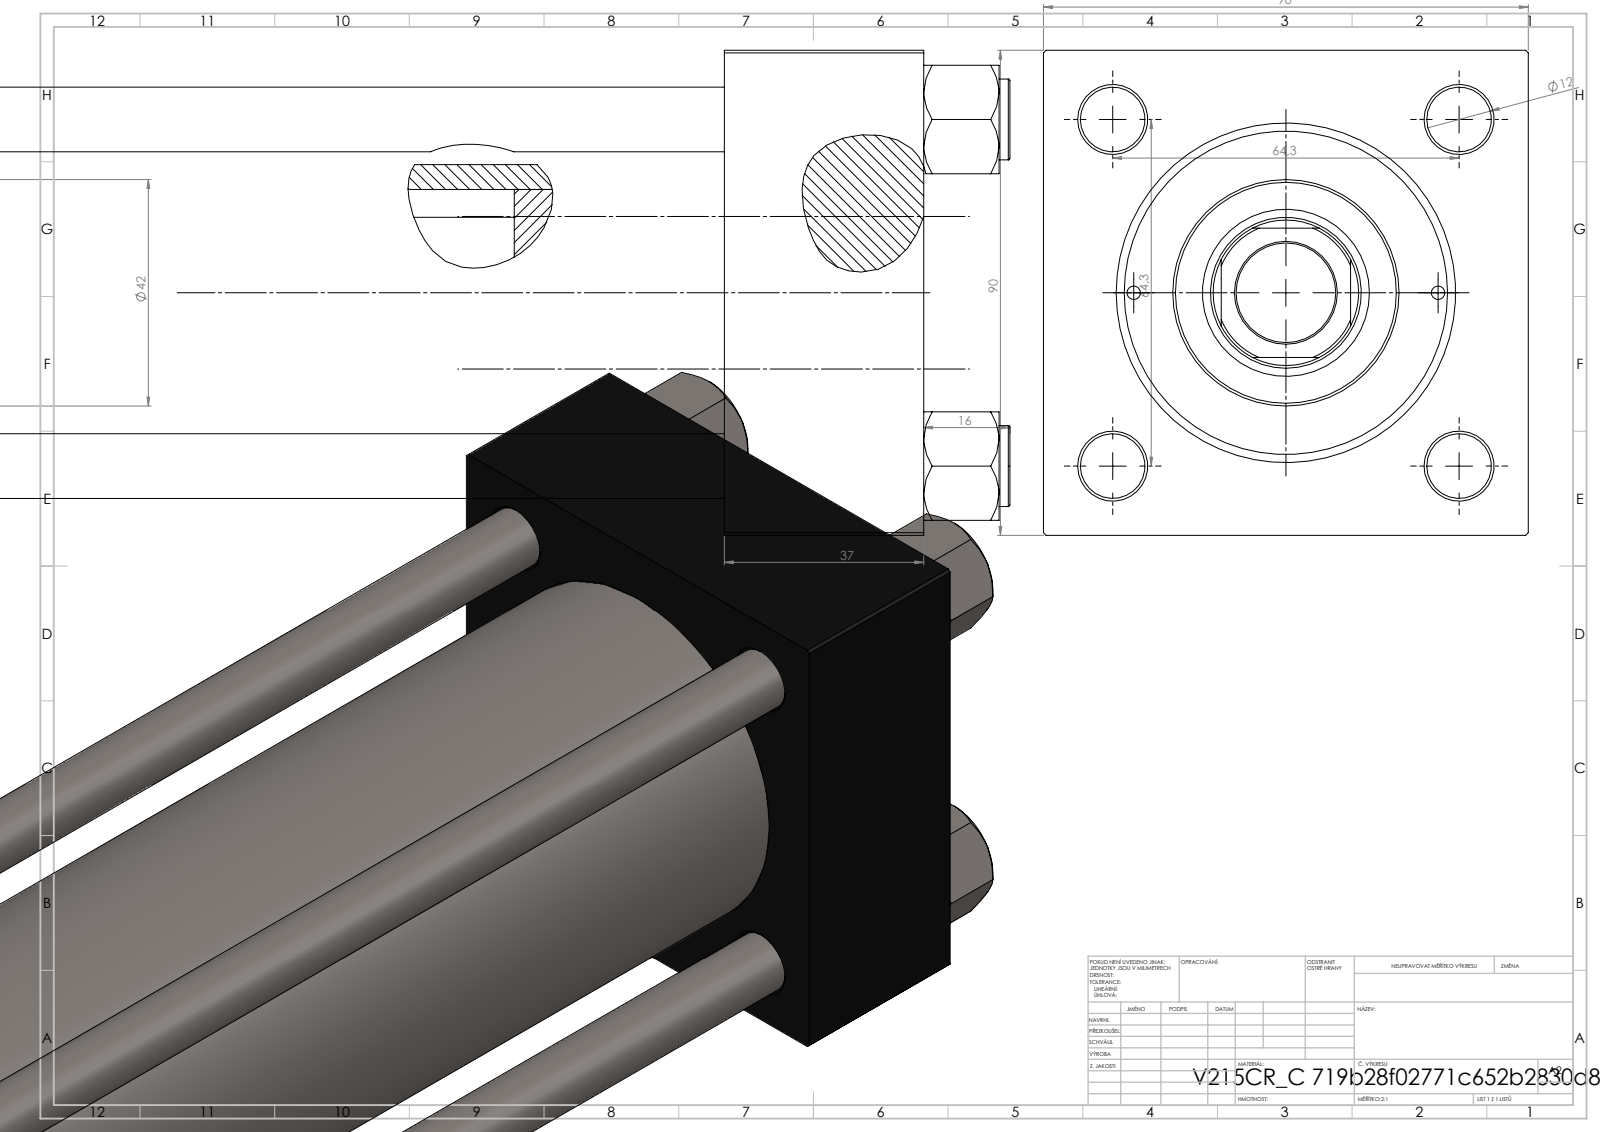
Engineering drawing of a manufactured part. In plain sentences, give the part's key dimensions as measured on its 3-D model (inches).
The part is named "V215CR_C_Body; NUT_M5_C; V215CR_C_TYCINKA; V215CR_VCP_C (+1 more)". Its 3-D file was written by "SolidWorks 2019 (CONFIG_CONTROL_DESIGN)". It is 11 solids with 1154 faces: 528 planar, 90 cylindrical and 536 other. Overall it measures 20.984 by 3.543 by 3.543 inches. Its volume is 91.84 cubic inches and its surface area 612 square inches. Round holes: 4 of diameter 0.472, 2 of diameter 0.098, 2 of diameter 0.276, 2 of diameter 0.825, 2 of diameter 1.181, 1 of diameter 0.728, 1 of diameter 1.102, 1 of diameter 1.22, 1 of diameter 1.969, 1 of diameter 2.362, 1 of diameter 2.48. Round bosses or shafts: 4 of diameter 0.591, 1 of diameter 2.717, 1 of diameter 1.654. Partial cylindrical surfaces (rounded edges, fillets, slot ends): 1 of radius 0.531. The main face-to-face distances are 3.543, 1.457, 19.094, 17.638, 16.772, 15.315, 2.323, 17.965, 16.508, 1.193. The hole center spacings are 1.275, 1.79, 2.531, 2.694, 1.112, 3.58, 2.224, 16.831.
